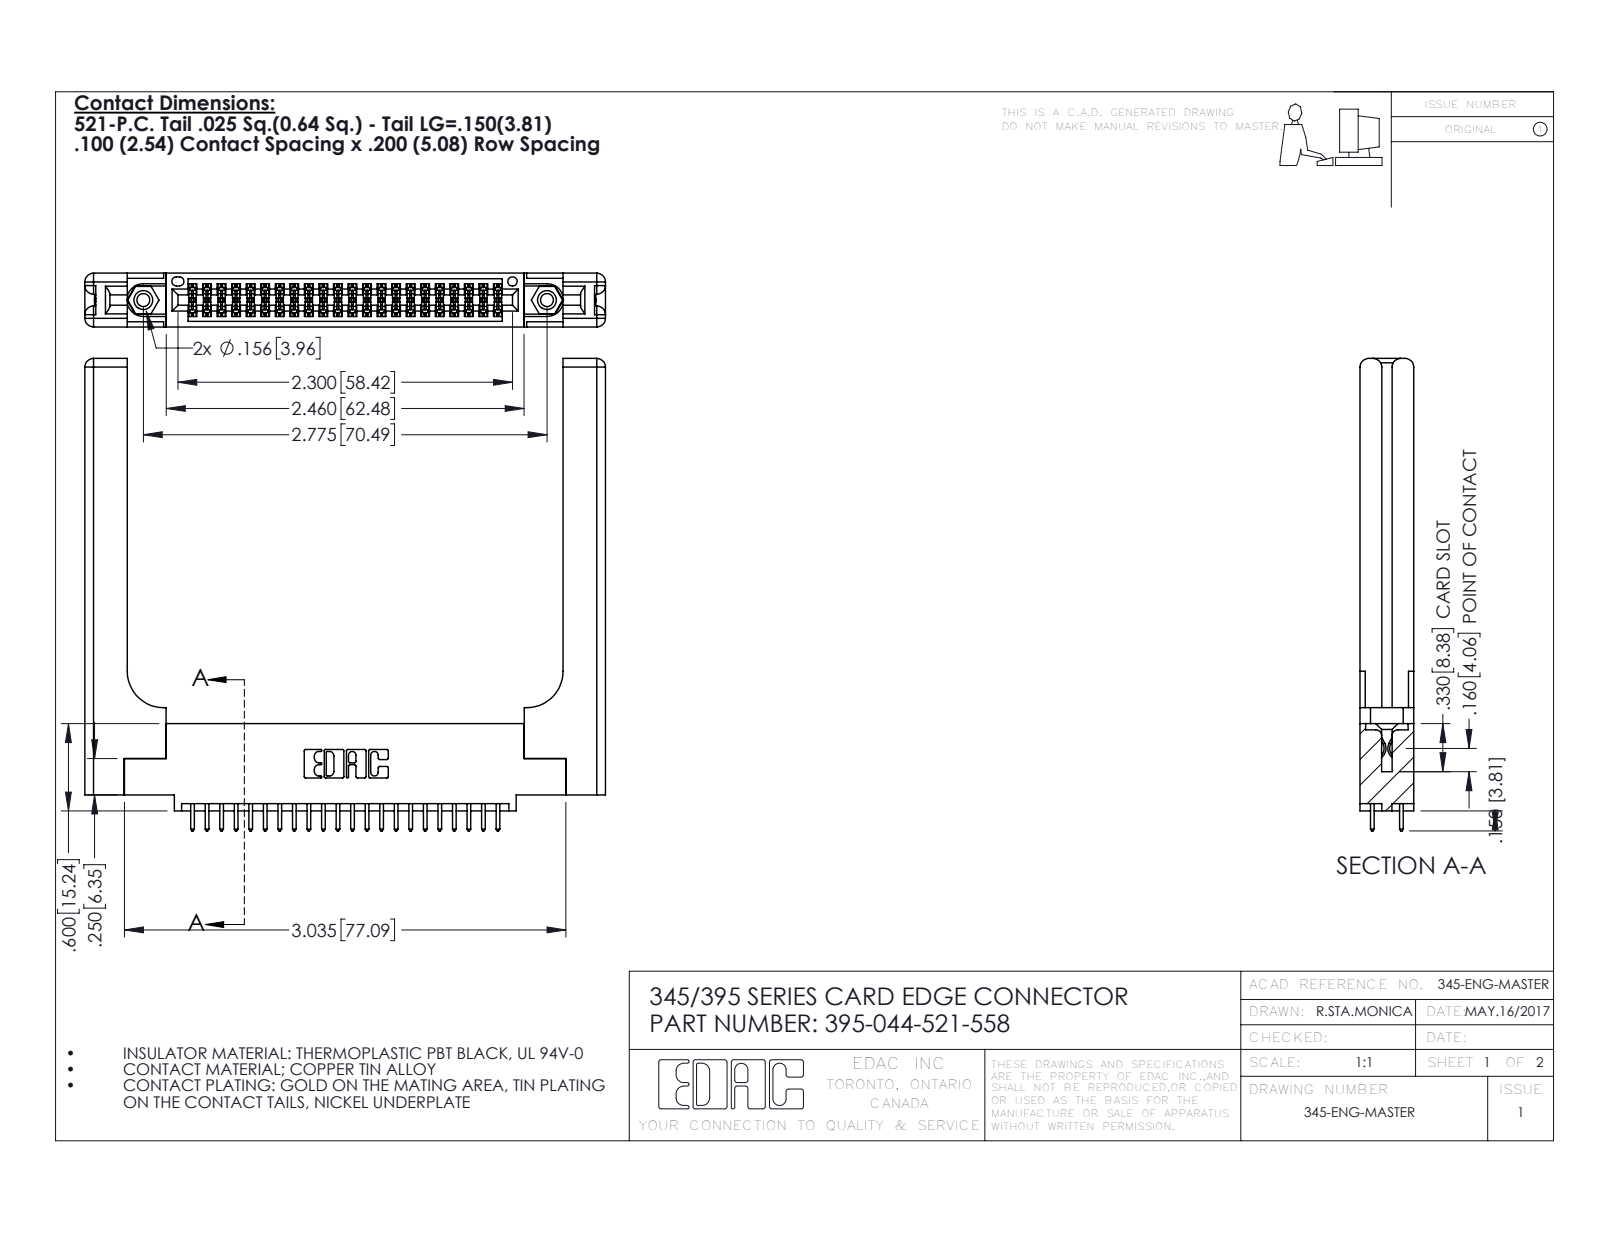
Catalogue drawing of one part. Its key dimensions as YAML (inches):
part_name: "345 Part_0.110 Offset - 0.156 Dia-TH; 395-044-521-558; 345-292-001_345-293-121; 345-220-058_345-220-058 (+1 more)"
step_written_by: "SolidWorks 2016 (CONFIG_CONTROL_DESIGN)"
units: inches
bodies: {solids: 49, faces: 2586, planar: 1684, cylindrical: 842, other: 60}
overall_size: [3.579, 3.247, 0.37]
volume: 1.039
surface_area: 26.8
round_holes:
  - {diameter: 0.089, count: 2}
  - {diameter: 0.125, count: 2}
  - {diameter: 0.156, count: 2}
  - {diameter: 0.064, count: 1}
round_bosses_or_shafts:
  - {diameter: 0.155, count: 2}
partial_cylinders:
  - {radius: 0.006, count: 66}
  - {radius: 0.01, count: 44}
  - {radius: 0.01, count: 22}
  - {radius: 0.06, count: 16}
  - {radius: 0.007, count: 6}
  - {radius: 0.031, count: 6}
  - {radius: 0.026, count: 3}
  - {radius: 0.014, count: 2}
face_to_face_distances: [0.37, 0.072, 0.298, 0.15, 0.148, 0.098, 0.272, 0.025, 0.2, 0.225]
hole_center_spacings: [0.27, 2.541, 2.775]
